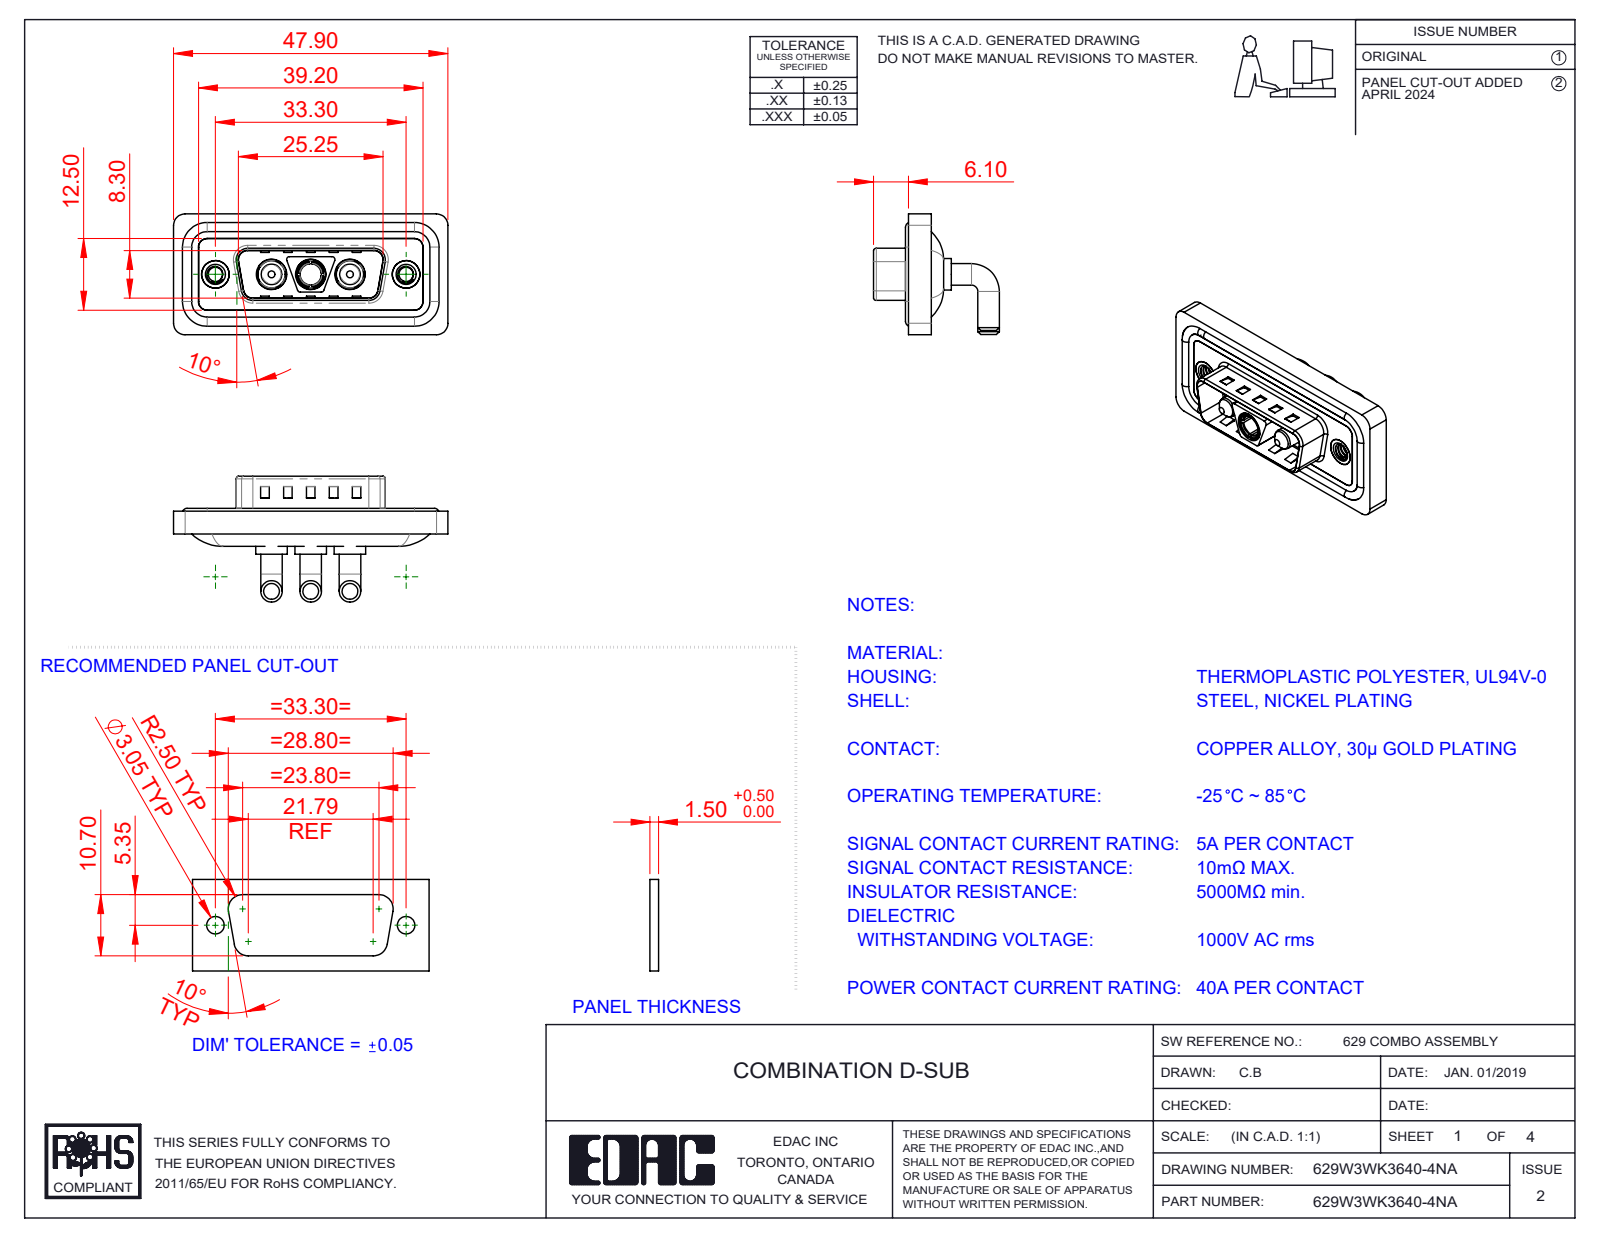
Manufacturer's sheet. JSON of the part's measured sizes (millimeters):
{"part_name": "629Combo Shell Front_15 Contacts; 629W3WK3640-4NA; 629Combo Housing_3WK3; Power Socket_40A RA (+4 more)", "step_written_by": "SolidWorks 2023 (CONFIG_CONTROL_DESIGN)", "units": "millimeters", "bodies": {"solids": 13, "faces": 615, "planar": 231, "cylindrical": 254, "other": 130}, "overall_size": [47.9, 21.98, 21.1], "volume_mm3": 6111, "surface_area_mm2": 9553, "round_holes": [[4.85, 3], [5.3, 3], [2.5, 2], [4, 2], [4.8, 2], [5, 2], [3.7, 1]], "round_bosses_or_shafts": [[3.75, 6], [1.6, 4], [5.5, 3], [5.2, 3], [4.75, 3], [4.9, 2], [3.6, 2], [4.96, 1]], "partial_cylinders_radius": [[2, 20], [1.5, 18], [0.5, 12], [1.6, 8], [0.25, 4], [0.6, 4], [0.65, 4], [0.9, 4]], "face_to_face_distances": [0.4, 2.9, 0.8, 1.1, 2.1, 1.6, 4.5, 3.1, 2.5, 3.7], "hole_center_spacings": [6.85, 9.8, 16.65, 23.5, 13.7, 33.3]}
